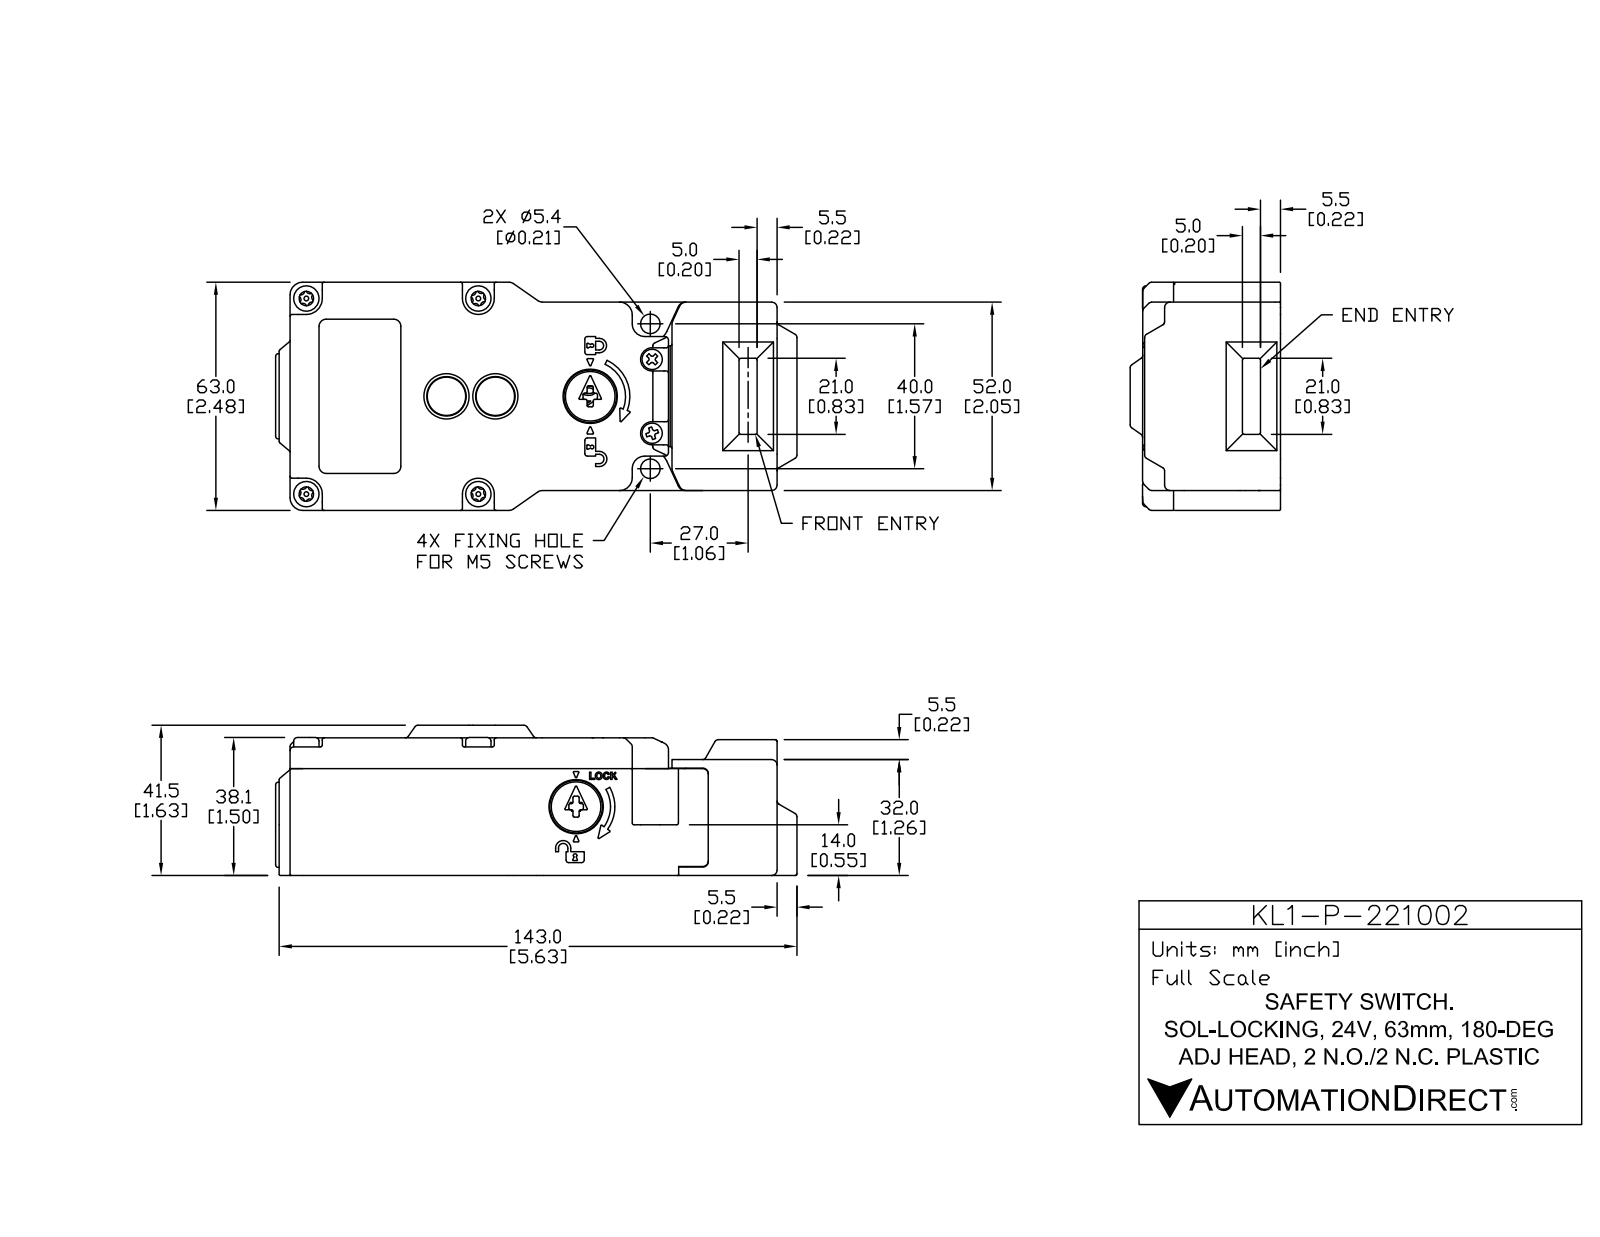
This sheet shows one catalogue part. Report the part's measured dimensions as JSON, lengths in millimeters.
{"part_name": "KL1-P-221002", "step_written_by": "SolidWorks 2017 (AUTOMOTIVE_DESIGN)", "units": "millimeters", "bodies": {"solids": 18, "faces": 3047, "planar": 909, "cylindrical": 1225, "other": 913}, "overall_size": [144, 63, 41.5], "volume_mm3": 104000, "surface_area_mm2": 76650, "round_holes": [[2.6, 4], [3.4, 4], [4, 4], [4.1, 4], [4.5, 4], [5, 4], [2, 2], [2.1, 2], [3, 2], [3.2, 2], [3.6, 2], [6.7, 2]], "round_bosses_or_shafts": [[7, 4], [3.5, 4], [1.3, 4], [5, 3], [1, 3], [14.5, 2], [10.6, 2], [9.2, 2]], "partial_cylinders_radius": [[0.5, 348], [0.3, 126], [1, 106], [0.2, 30], [0.4, 24], [1.5, 16], [0.2, 14], [0.7, 12]], "face_to_face_distances": [2.5, 3, 5.5, 38, 35.5, 35.6, 33.1, 2.4, 57.5, 54.5], "hole_center_spacings": [10.3, 12.6, 13.1, 13.9, 19.9, 20.4, 27.4, 28.4]}
